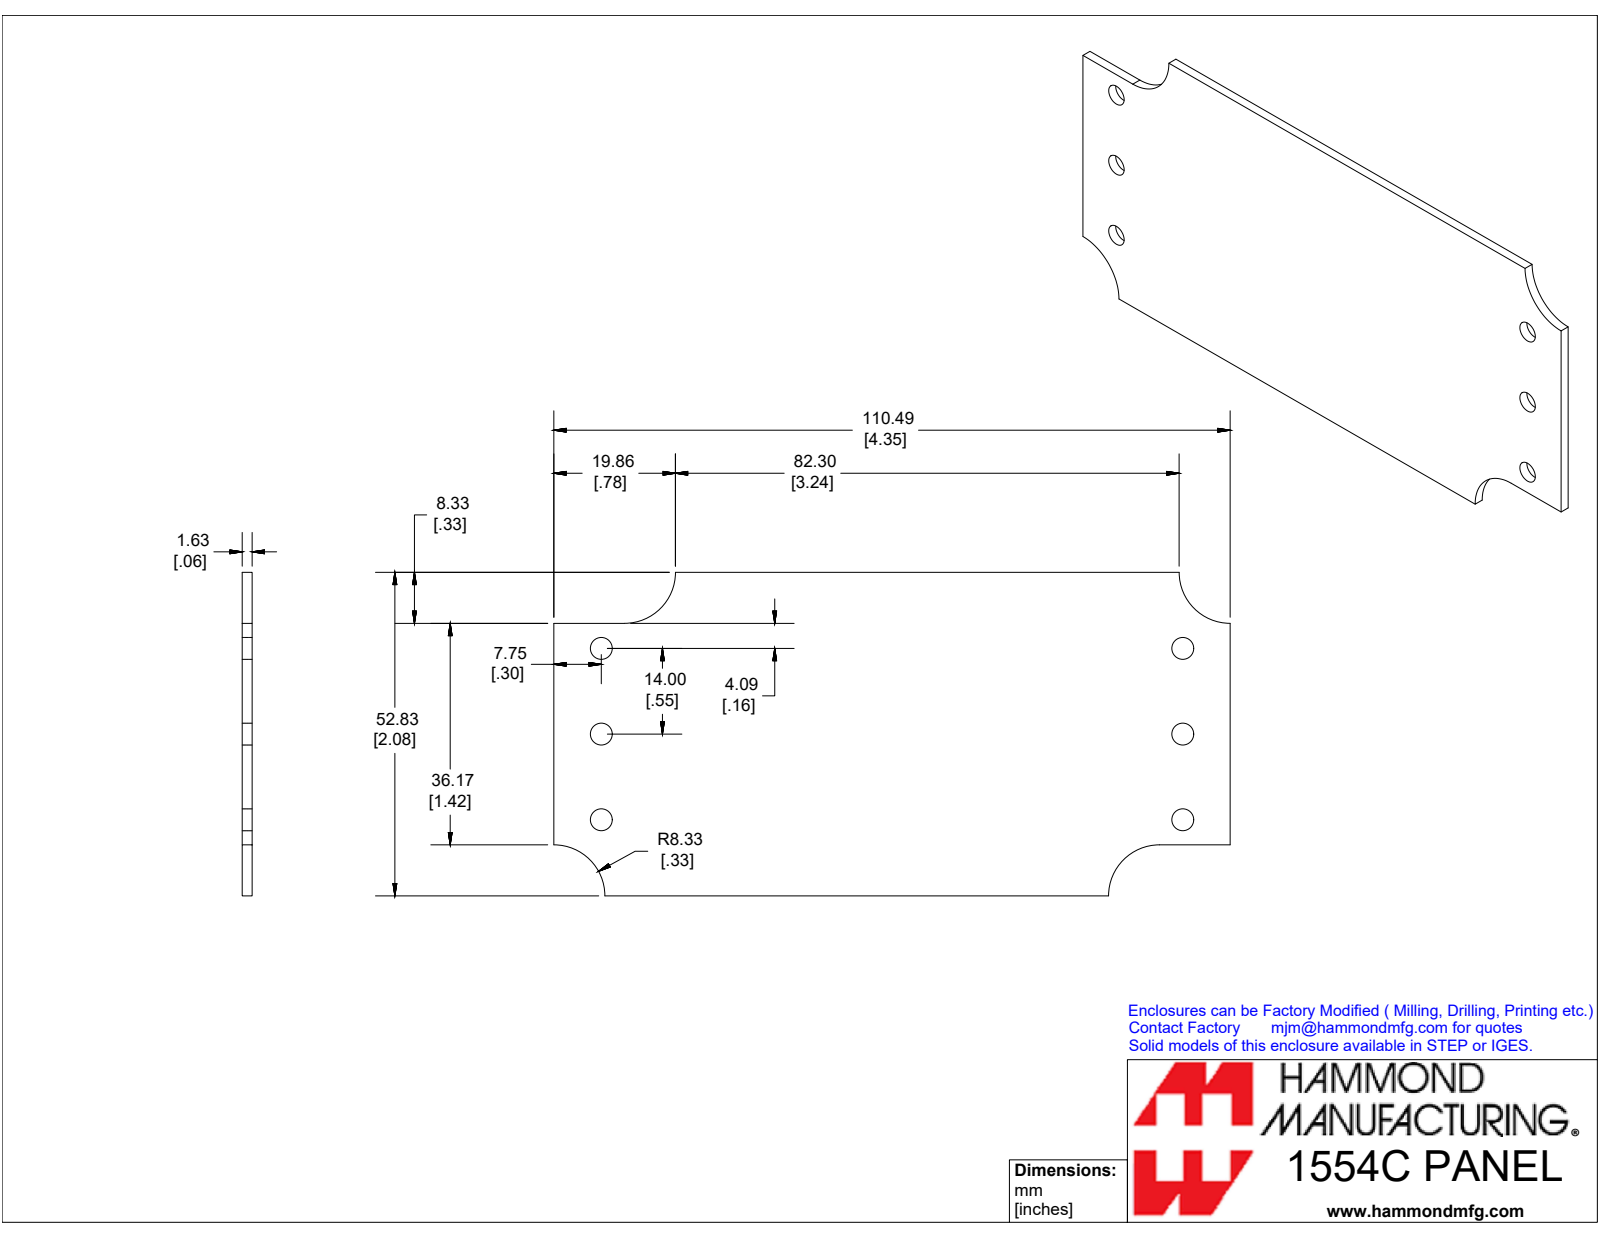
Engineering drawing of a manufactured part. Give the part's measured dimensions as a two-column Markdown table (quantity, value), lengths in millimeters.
| quantity | value |
| --- | --- |
| part name | 1554CPL |
| STEP written by | SolidWorks 2019 (CONFIG_CONTROL_DESIGN) |
| units | millimeters |
| bodies | 1 solid, 18 faces (8 planar, 10 cylindrical, 0 other) |
| overall size | 110.5 × 52.8 × 1.6 |
| volume | 8 720 mm³ |
| surface area | 11 350 mm² |
| round holes (diameter × count) | 3.7 × 6 |
| partial cylindrical surfaces (radius × count) | 8.3 × 4 |
| main face-to-face distances | 1.6, 52.8, 110.5, 8.3, 44.5, 36.2 |
| hole center spacings | 14, 96, 95, 28, 99 |
